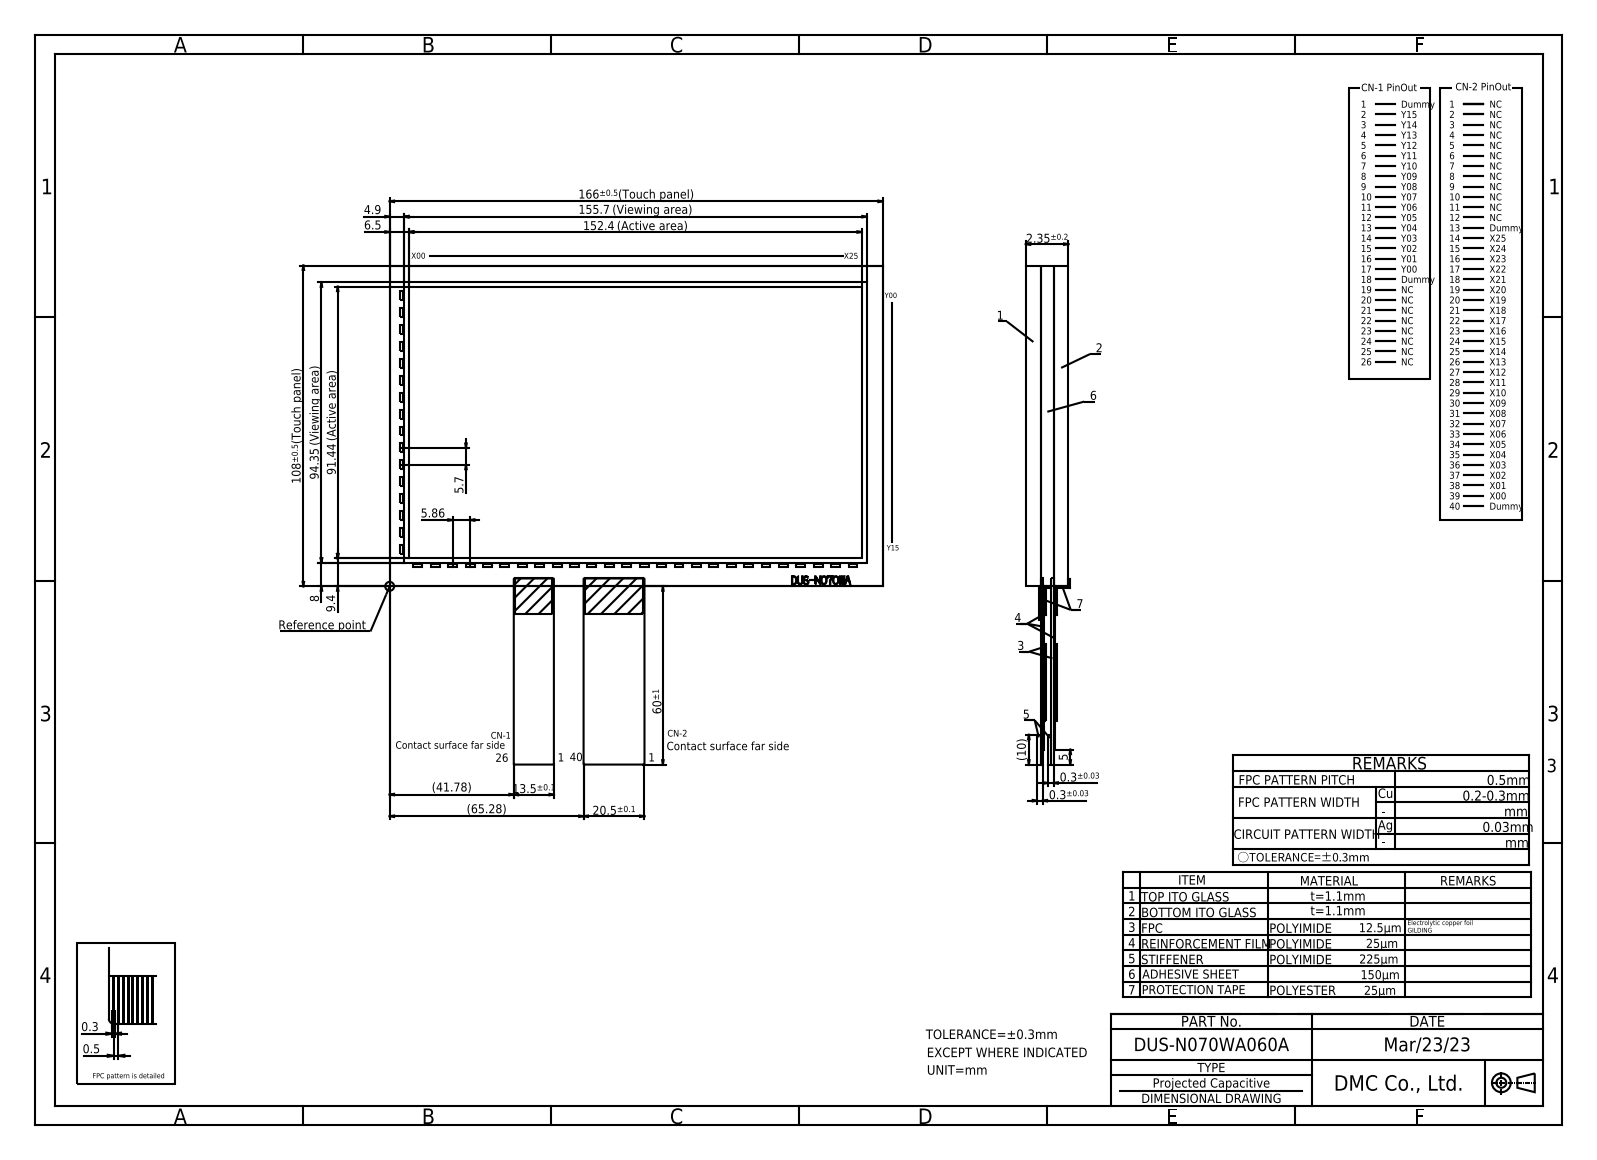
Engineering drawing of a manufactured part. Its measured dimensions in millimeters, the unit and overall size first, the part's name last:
Units: millimetres
Overall size (bounding box): 232.4 × 189.6 × 2.35
Partial cylindrical surfaces — rounded edges, fillets, slot ends (radius × count): R0.2 ×4
Main face-to-face distances: 2.35, 1.2, 1.15, 1.25, 1.1, 108, 0.8, 1.55, 0.4, 166
Volume: 42 419 mm³ · Surface area: 41 284 mm²
Bodies: 1 solid, 292 faces (288 planar, 4 cylindrical, 0 other)
Part name (STEP PRODUCT): DUS-N070WA060A
STEP written by: Autodesk Inventor 2020 (AUTOMOTIVE_DESIGN)
